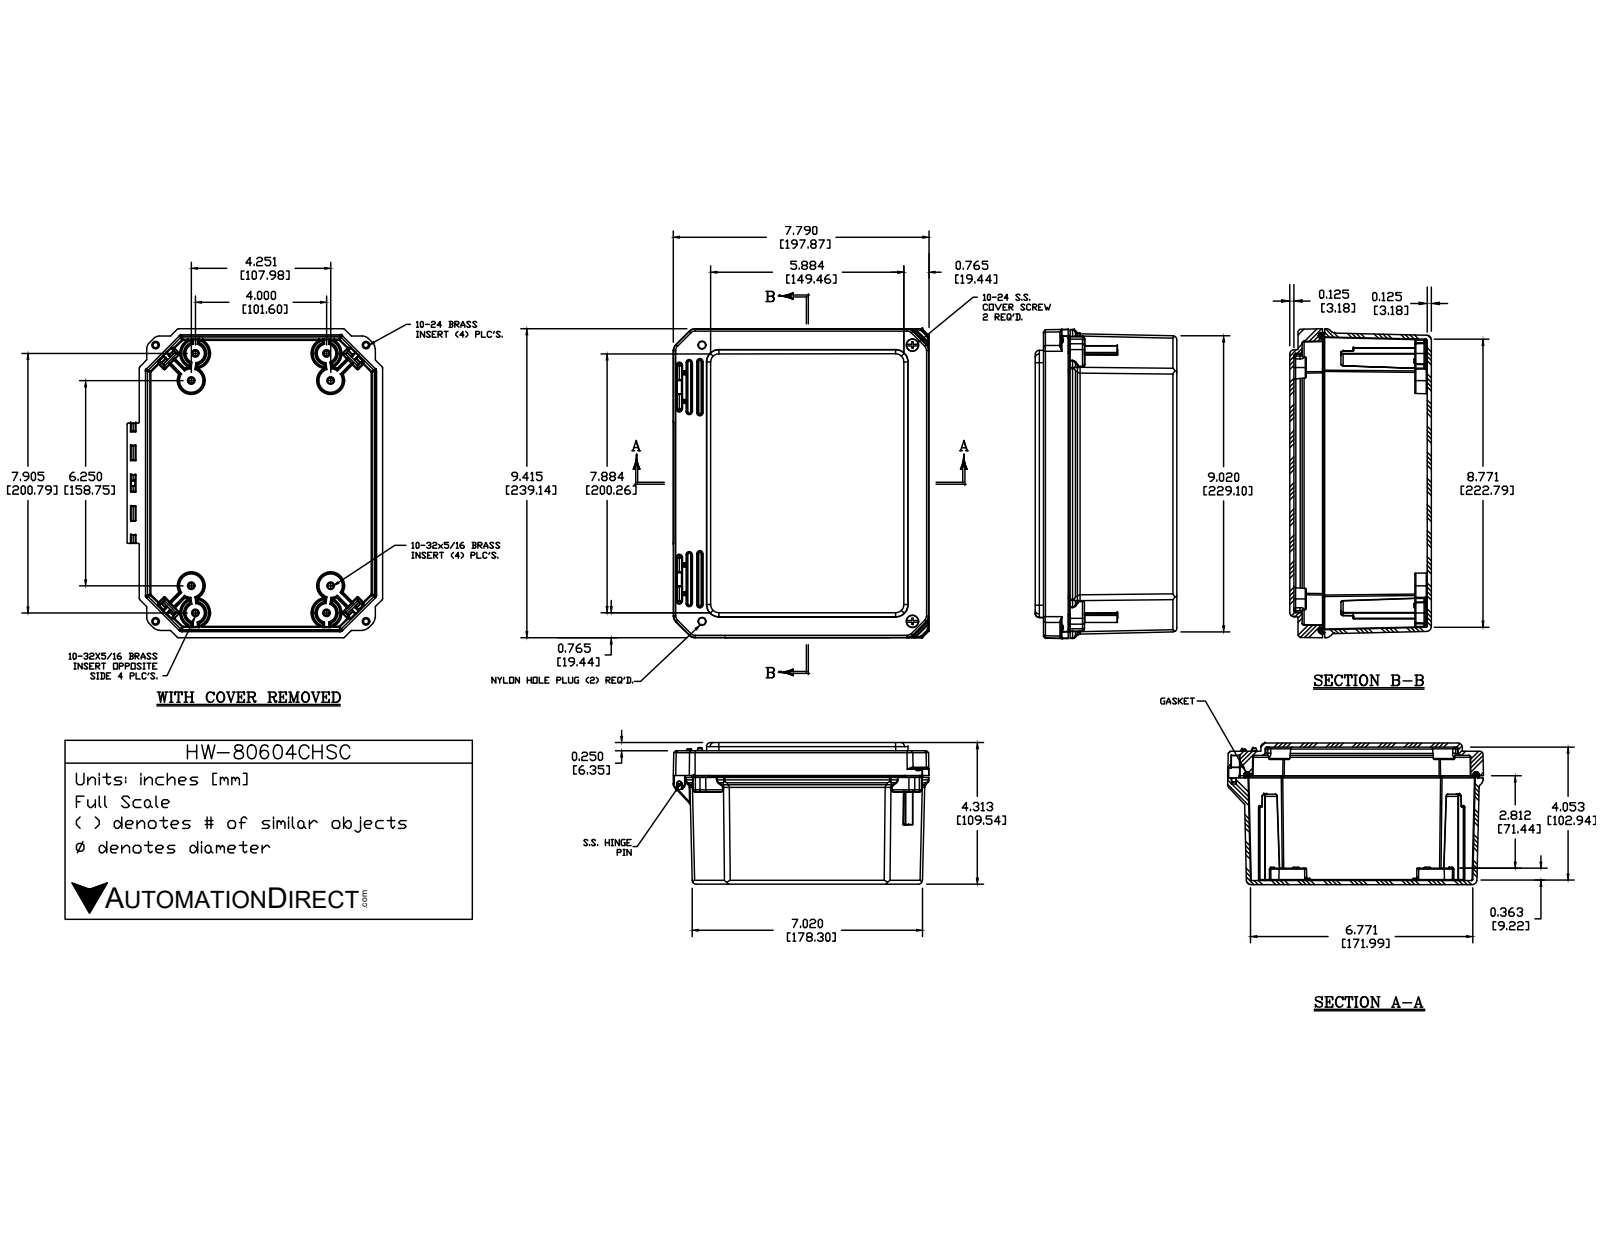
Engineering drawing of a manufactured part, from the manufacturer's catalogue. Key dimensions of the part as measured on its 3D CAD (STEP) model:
Part name (STEP PRODUCT): DS080604BOX; BRASS INSERT-(; BRASS INSERT-(_1; BRASS INSERT-(_2 (+8 more)
STEP written by: Autodesk Inventor 2014 (AUTOMOTIVE_DESIGN)
Units: millimetres
Bodies: 29 solids, 2182 faces (705 planar, 827 cylindrical, 650 other)
Overall size (bounding box): 239.14 × 197.87 × 109.48
Volume: 732 864 mm³ · Surface area: 393 570 mm²
Round holes (diameter × count): ⌀3.96 ×16, ⌀3.86 ×8, ⌀6.4 ×4, ⌀6.43 ×4, ⌀3.81 ×2, ⌀5.56 ×2, ⌀5.77 ×2, ⌀7.94 ×2, ⌀3.48 ×1
Round bosses / shafts (diameter × count): ⌀6.25 ×16, ⌀22.1 ×4, ⌀11.43 ×2, ⌀11.05 ×2, ⌀5.3 ×2, ⌀5.05 ×2, ⌀3.43 ×1
Partial cylindrical surfaces — rounded edges, fillets, slot ends (radius × count): R0.25 ×150, R0.51 ×92, R0.13 ×80, R0.76 ×43, R1.59 ×27, R0.76 ×24, R2.29 ×24, R2.44 ×24
Main face-to-face distances: 3.17, 106.31, 109.48, 103.14, 6.35, 3.15, 99.96, 3.18, 103.13, 9.53
Hole centre spacings: 38.88, 208.09, 230.26, 230.29, 21.27, 38.85, 106.86, 138.16
